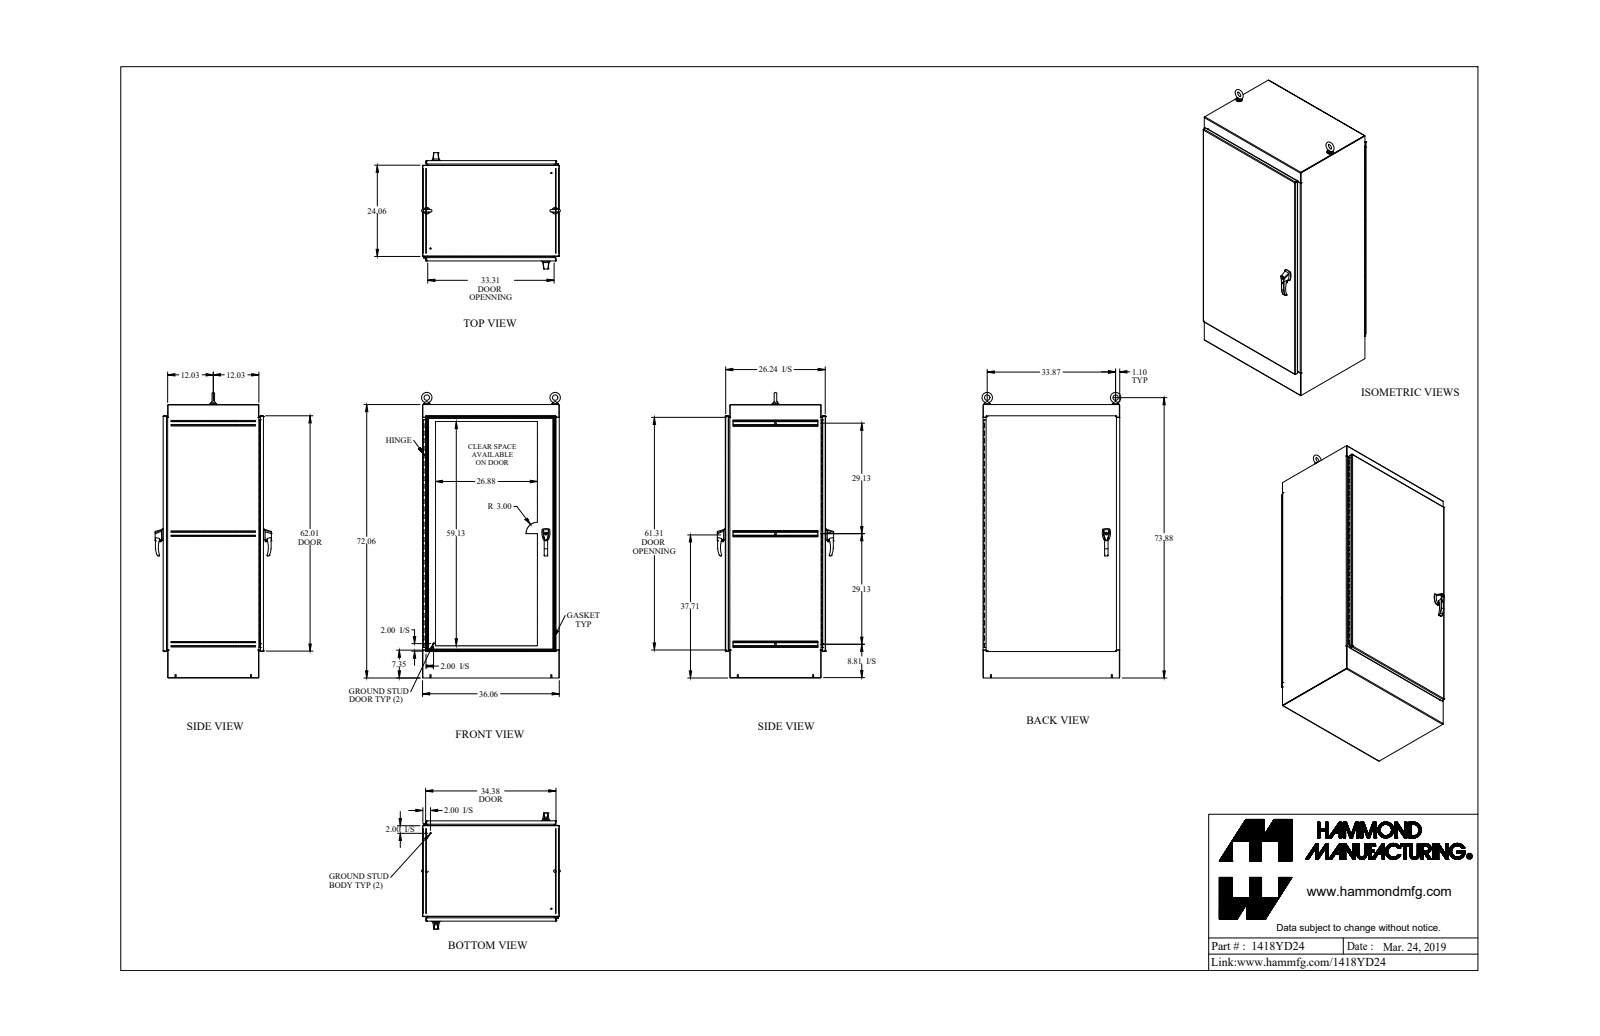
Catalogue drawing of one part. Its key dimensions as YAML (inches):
part_name: "1418YD24_Default"
step_written_by: "SolidWorks 2019 (CONFIG_CONTROL_DESIGN)"
units: inches
bodies: {solids: 83, faces: 3051, planar: 1358, cylindrical: 1427, other: 266}
overall_size: [75.713, 37.119, 30.664]
volume: 1245
surface_area: 26327
round_holes:
  - {diameter: 0.304, count: 20}
  - {diameter: 0.25, count: 4}
  - {diameter: 0.257, count: 4}
  - {diameter: 0.28, count: 4}
  - {diameter: 0.281, count: 4}
  - {diameter: 0.313, count: 4}
  - {diameter: 0.39, count: 4}
  - {diameter: 0.413, count: 4}
  - {diameter: 0.5, count: 3}
  - {diameter: 0.11, count: 2}
  - {diameter: 0.173, count: 2}
  - {diameter: 0.233, count: 2}
round_bosses_or_shafts:
  - {diameter: 0.281, count: 8}
  - {diameter: 1, count: 4}
  - {diameter: 0.75, count: 4}
  - {diameter: 0.63, count: 4}
  - {diameter: 0.625, count: 4}
  - {diameter: 0.44, count: 4}
  - {diameter: 0.37, count: 4}
  - {diameter: 0.25, count: 4}
partial_cylinders:
  - {radius: 0.125, count: 44}
  - {radius: 0.043, count: 42}
  - {radius: 0.138, count: 36}
  - {radius: 0.018, count: 32}
  - {radius: 0.048, count: 24}
  - {radius: 0.143, count: 24}
  - {radius: 0.06, count: 16}
  - {radius: 0.318, count: 14}
face_to_face_distances: [0.095, 26.339, 35.965, 26.244, 26.434, 1.187, 25.152, 35.87, 36.06, 71.965]
hole_center_spacings: [6, 34.853, 12, 36.369, 18, 38.765, 24, 41.889]
